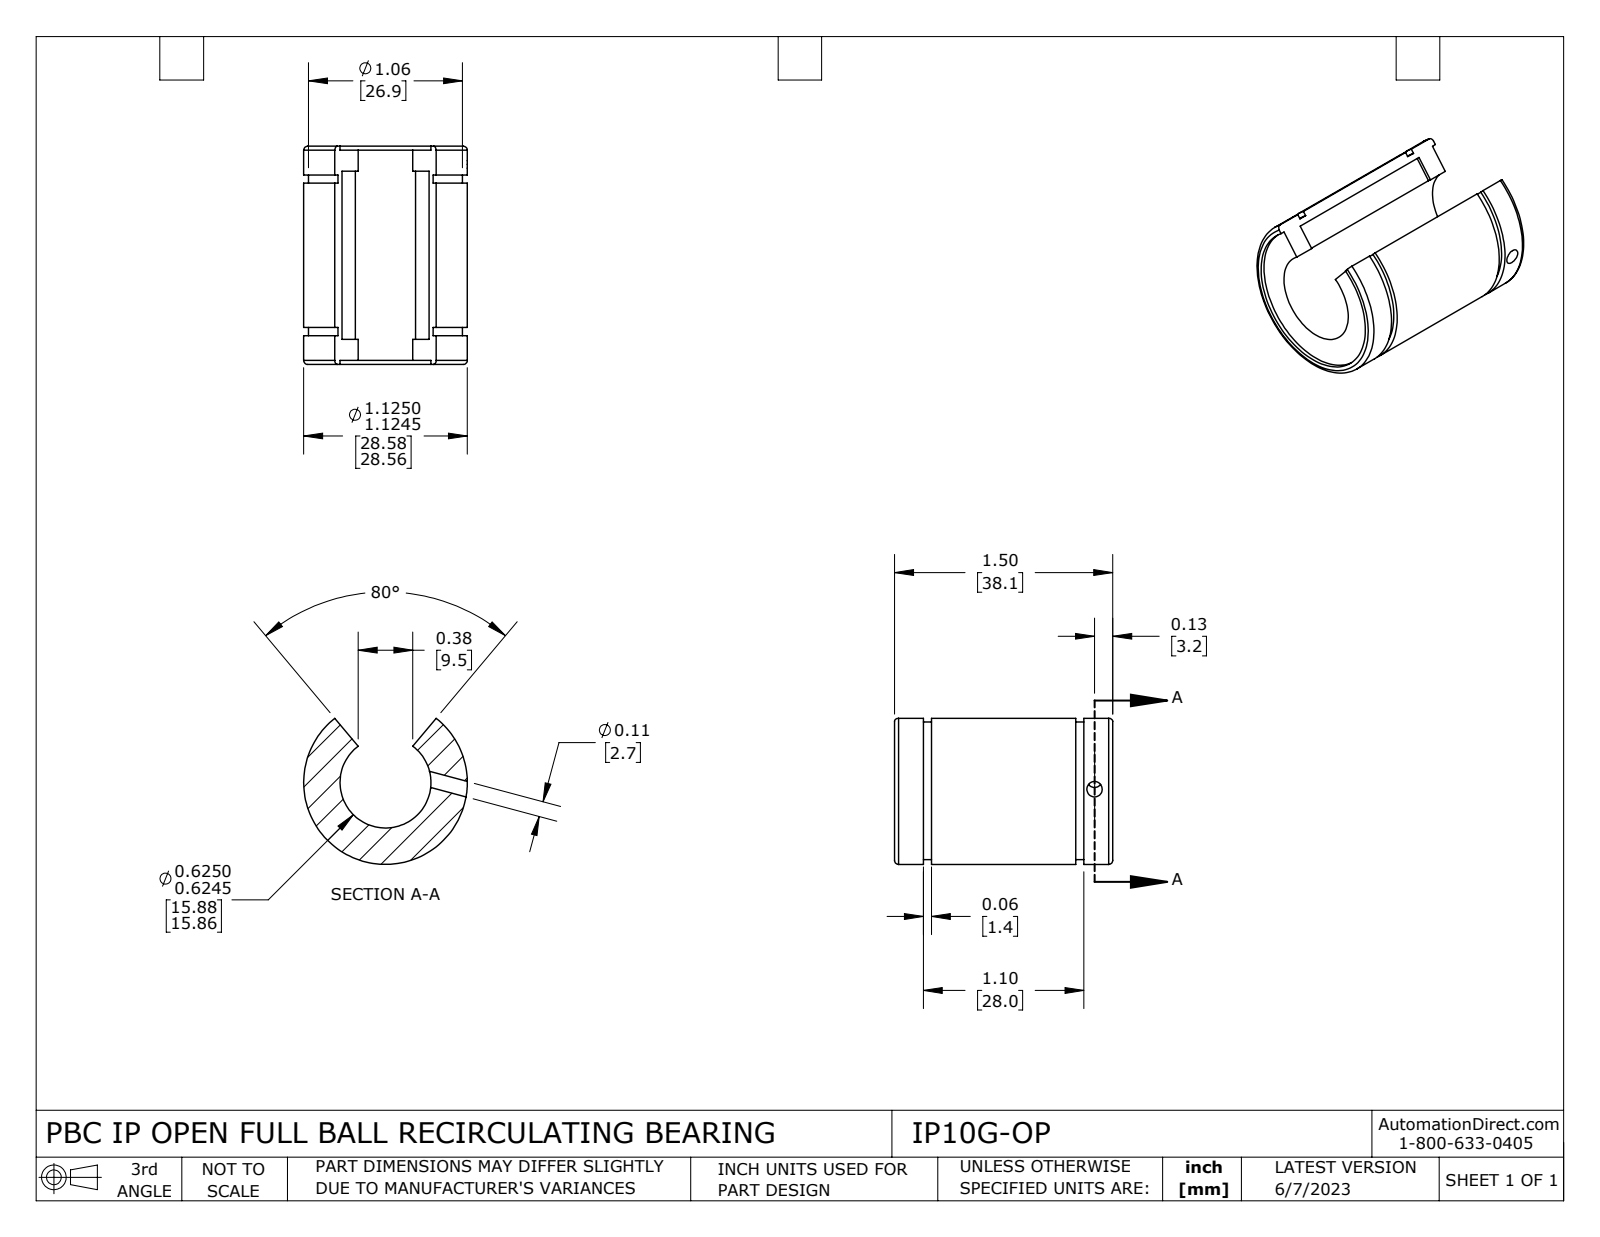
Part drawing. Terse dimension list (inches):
name: IP10G-OP
written by: SolidWorks 2021 (CONFIG_CONTROL_DESIGN)
unit: in
bodies: 1 solid, 40 faces (16 planar, 20 cylindrical, 4 other)
size: 1.5 × 1.125 × 1.004
volume: 0.769 in³; area: 8.732 in²
holes: 1× ⌀0.105, 1× ⌀0.625
rounds: 1× R0.486, 1× R0.507, 1× R0.529, 1× R0.562
face distances: 1.444, 0.17, 1.274, 0.226, 1.218, 1.048, 0.056, 0.025, 0.025, 0.028
